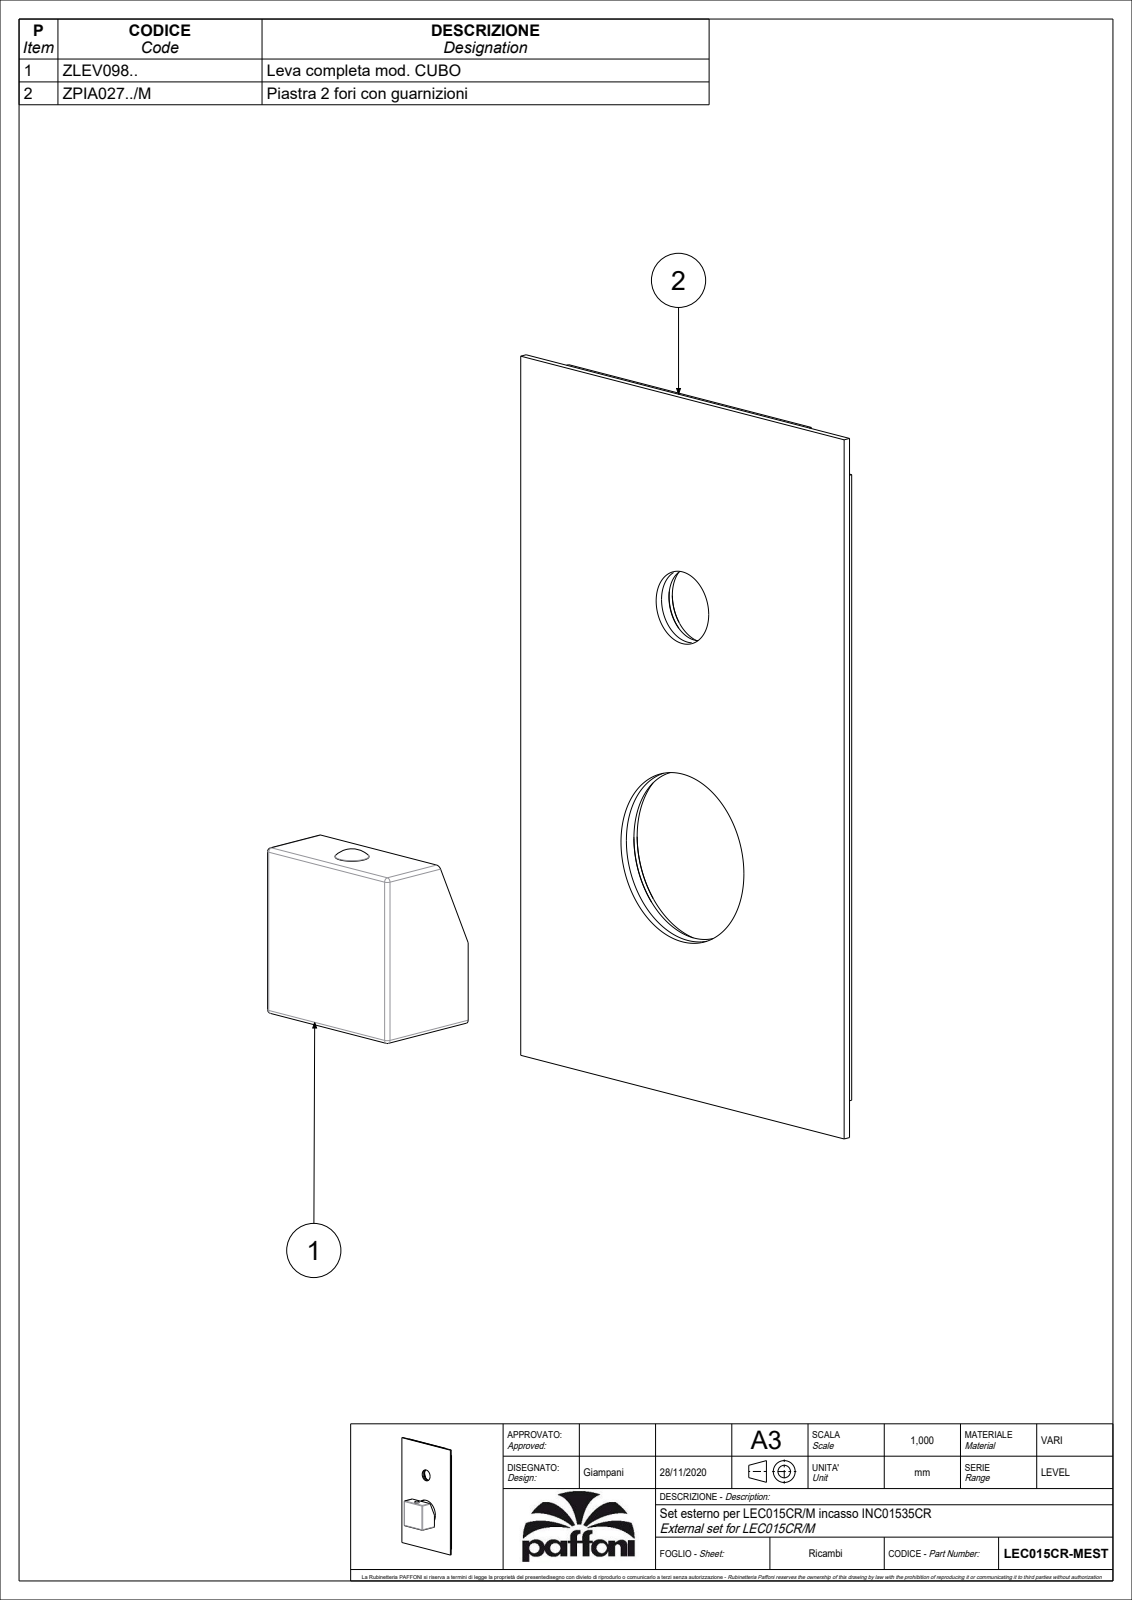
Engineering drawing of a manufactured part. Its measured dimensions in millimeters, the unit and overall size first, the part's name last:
Units: millimetres
Overall size (bounding box): 190 × 120 × 39.5
Round holes (diameter × count): ⌀6 ×1, ⌀8 ×1, ⌀19.5 ×1, ⌀21.5 ×1, ⌀25 ×1, ⌀45.6 ×1, ⌀47.6 ×1, ⌀51.1 ×1
Round bosses / shafts (diameter × count): ⌀54.6 ×1, ⌀28.5 ×1, ⌀5 ×1
Partial cylindrical surfaces — rounded edges, fillets, slot ends (radius × count): R0.5 ×19, R1 ×16
Main face-to-face distances: 2, 0.8, 2.8, 34.8, 3, 45, 34, 32, 29, 31.8
Hole centre spacings: 68
Volume: 63 516 mm³ · Surface area: 62 910 mm²
Bodies: 2 solids, 192 faces (80 planar, 70 cylindrical, 42 other)
Part name (STEP PRODUCT): LEC015CR-MEST
STEP written by: CREO PARAMETRIC BY PTC INC, 2020044 (CONFIG_CONTROL_DESIGN)
